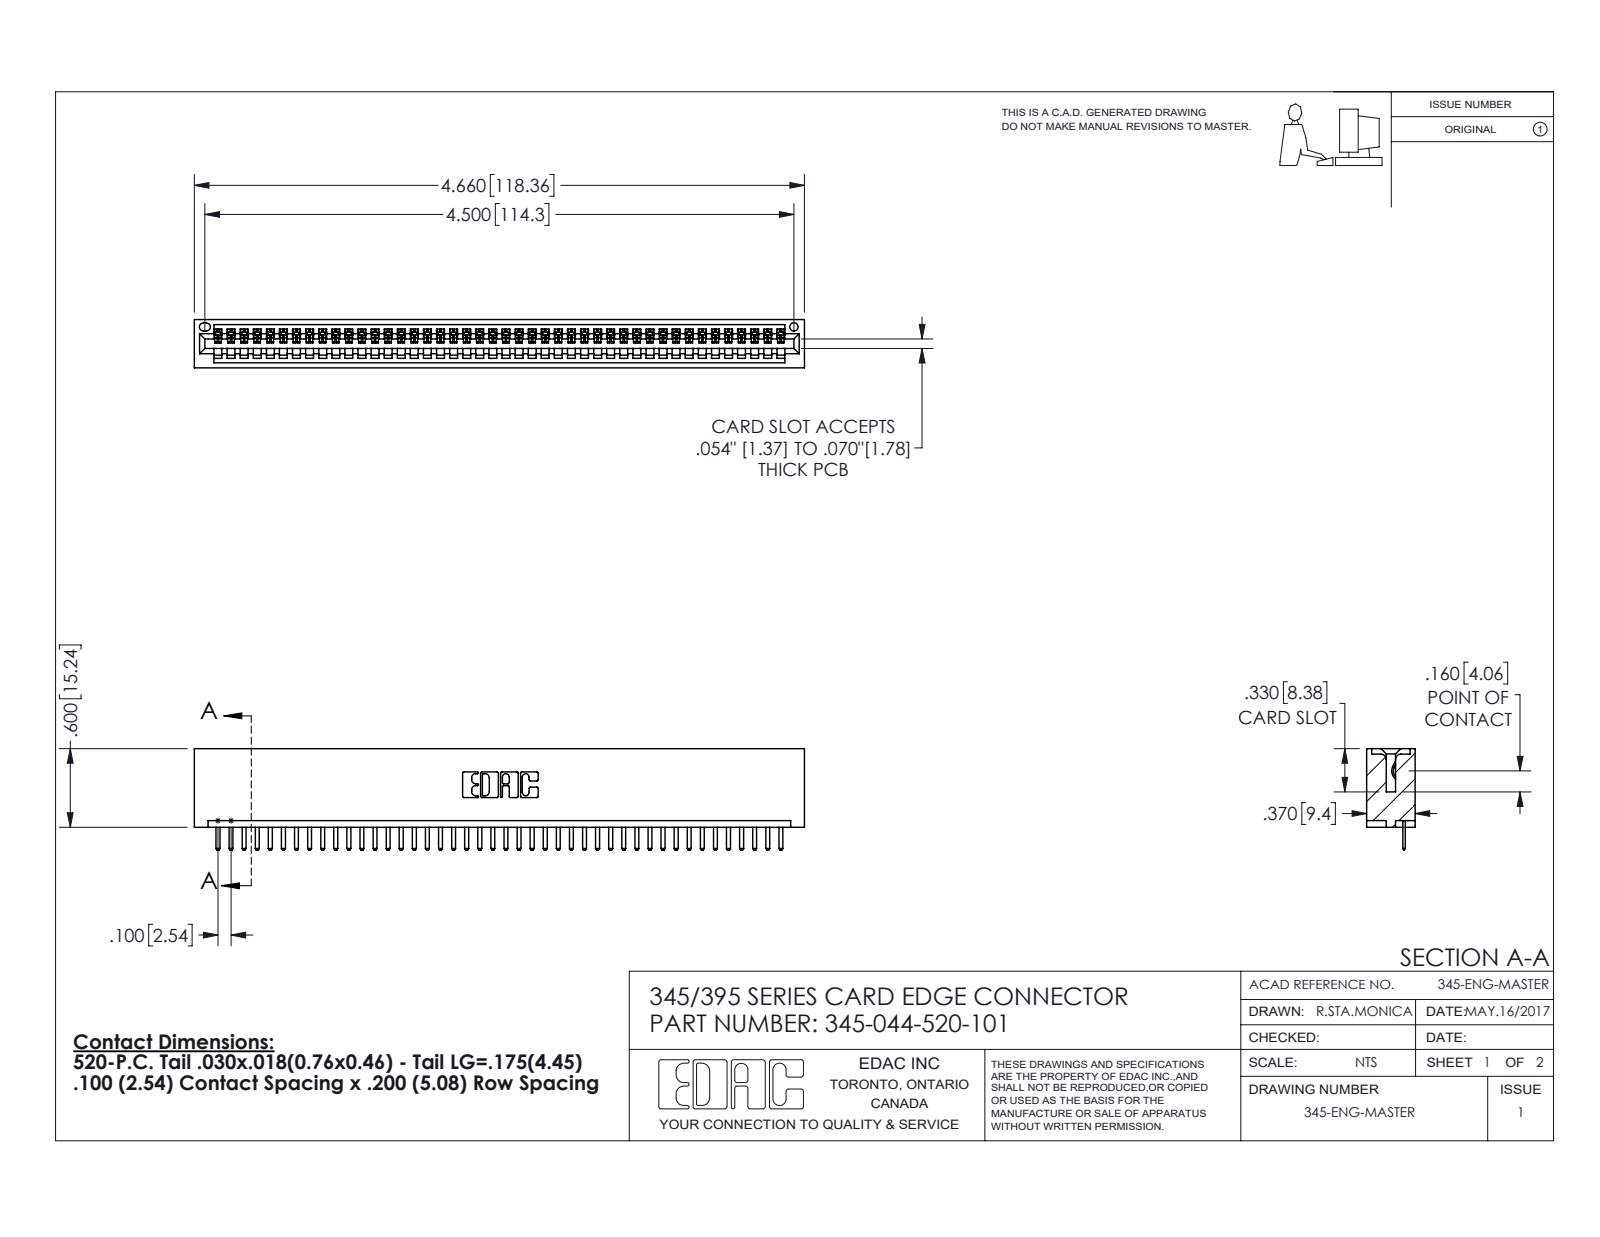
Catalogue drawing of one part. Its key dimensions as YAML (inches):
part_name: "345 Part_No Mounting Lugs; 345-044-520-101; 345-292-001_345-293-120"
step_written_by: "SolidWorks 2016 (CONFIG_CONTROL_DESIGN)"
units: inches
bodies: {solids: 45, faces: 2846, planar: 1924, cylindrical: 922, other: 0}
overall_size: [4.66, 0.775, 0.37]
volume: 0.715
surface_area: 23.83
round_holes:
  - {diameter: 0.064, count: 1}
partial_cylinders:
  - {radius: 0.01, count: 90}
  - {radius: 0.006, count: 88}
  - {radius: 0.01, count: 22}
  - {radius: 0.007, count: 6}
  - {radius: 0.031, count: 6}
  - {radius: 0.026, count: 3}
  - {radius: 0.031, count: 2}
  - {radius: 0.04, count: 2}
face_to_face_distances: [0.298, 0.072, 0.37, 0.2, 0.098, 0.272, 0.025, 0.225, 0.072, 0.149]
